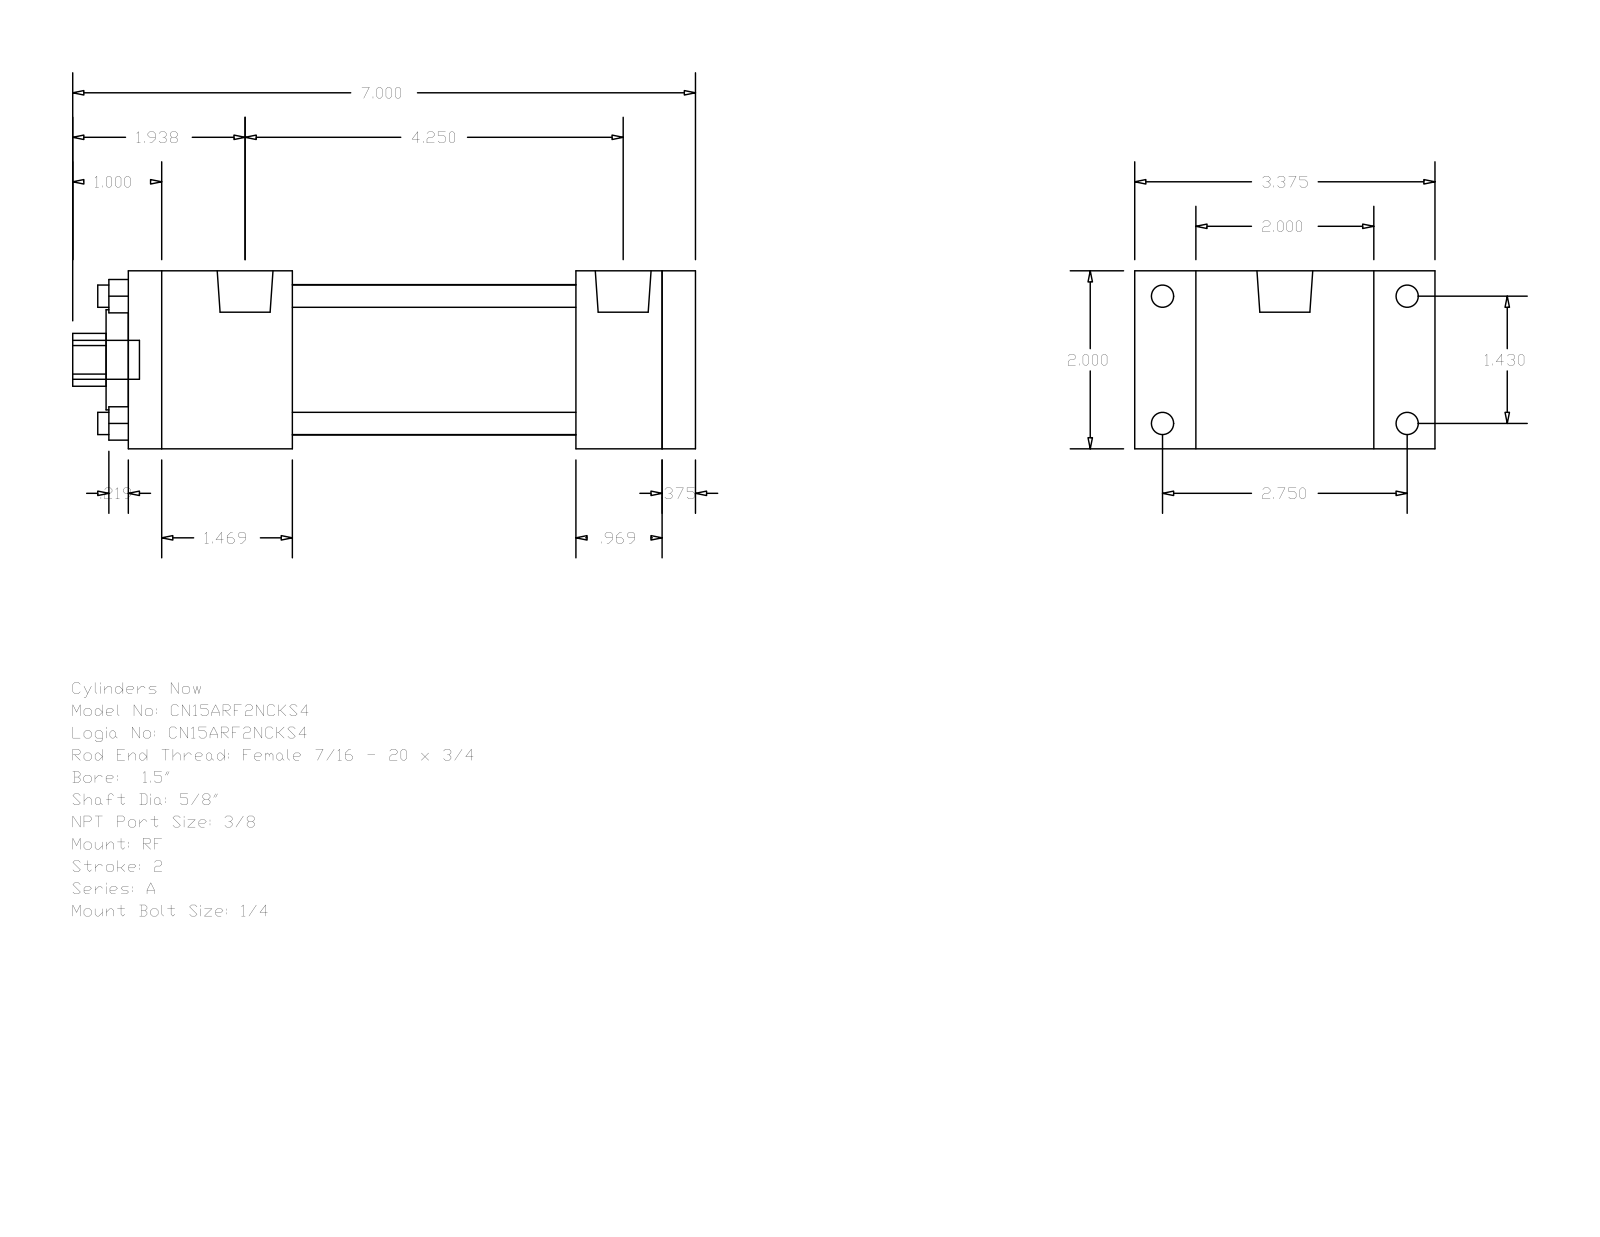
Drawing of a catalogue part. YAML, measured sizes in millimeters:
part_name: "A_RF__0150_0.625"
step_written_by: "GSSL Pune (CONFIG_CONTROL_DESIGN)"
units: millimeters
bodies: {solids: 0, faces: 92, planar: 64, cylindrical: 28, other: 0}
overall_size: [177.8, 85.72, 50.8]
round_holes:
  - {diameter: 6.35, count: 4}
  - {diameter: 15.88, count: 1}
  - {diameter: 28.57, count: 1}
  - {diameter: 42.93, count: 1}
round_bosses_or_shafts:
  - {diameter: 6.35, count: 4}
  - {diameter: 5.56, count: 4}
  - {diameter: 15.93, count: 2}
  - {diameter: 11.11, count: 1}
partial_cylinders:
  - {radius: 7.54, count: 1}
face_to_face_distances: [50.8, 9.52, 152.4, 161.92, 127.79, 24.61, 34.13, 46.83, 80.96, 105.57]
hole_center_spacings: [25.68, 36.32, 51.36]
